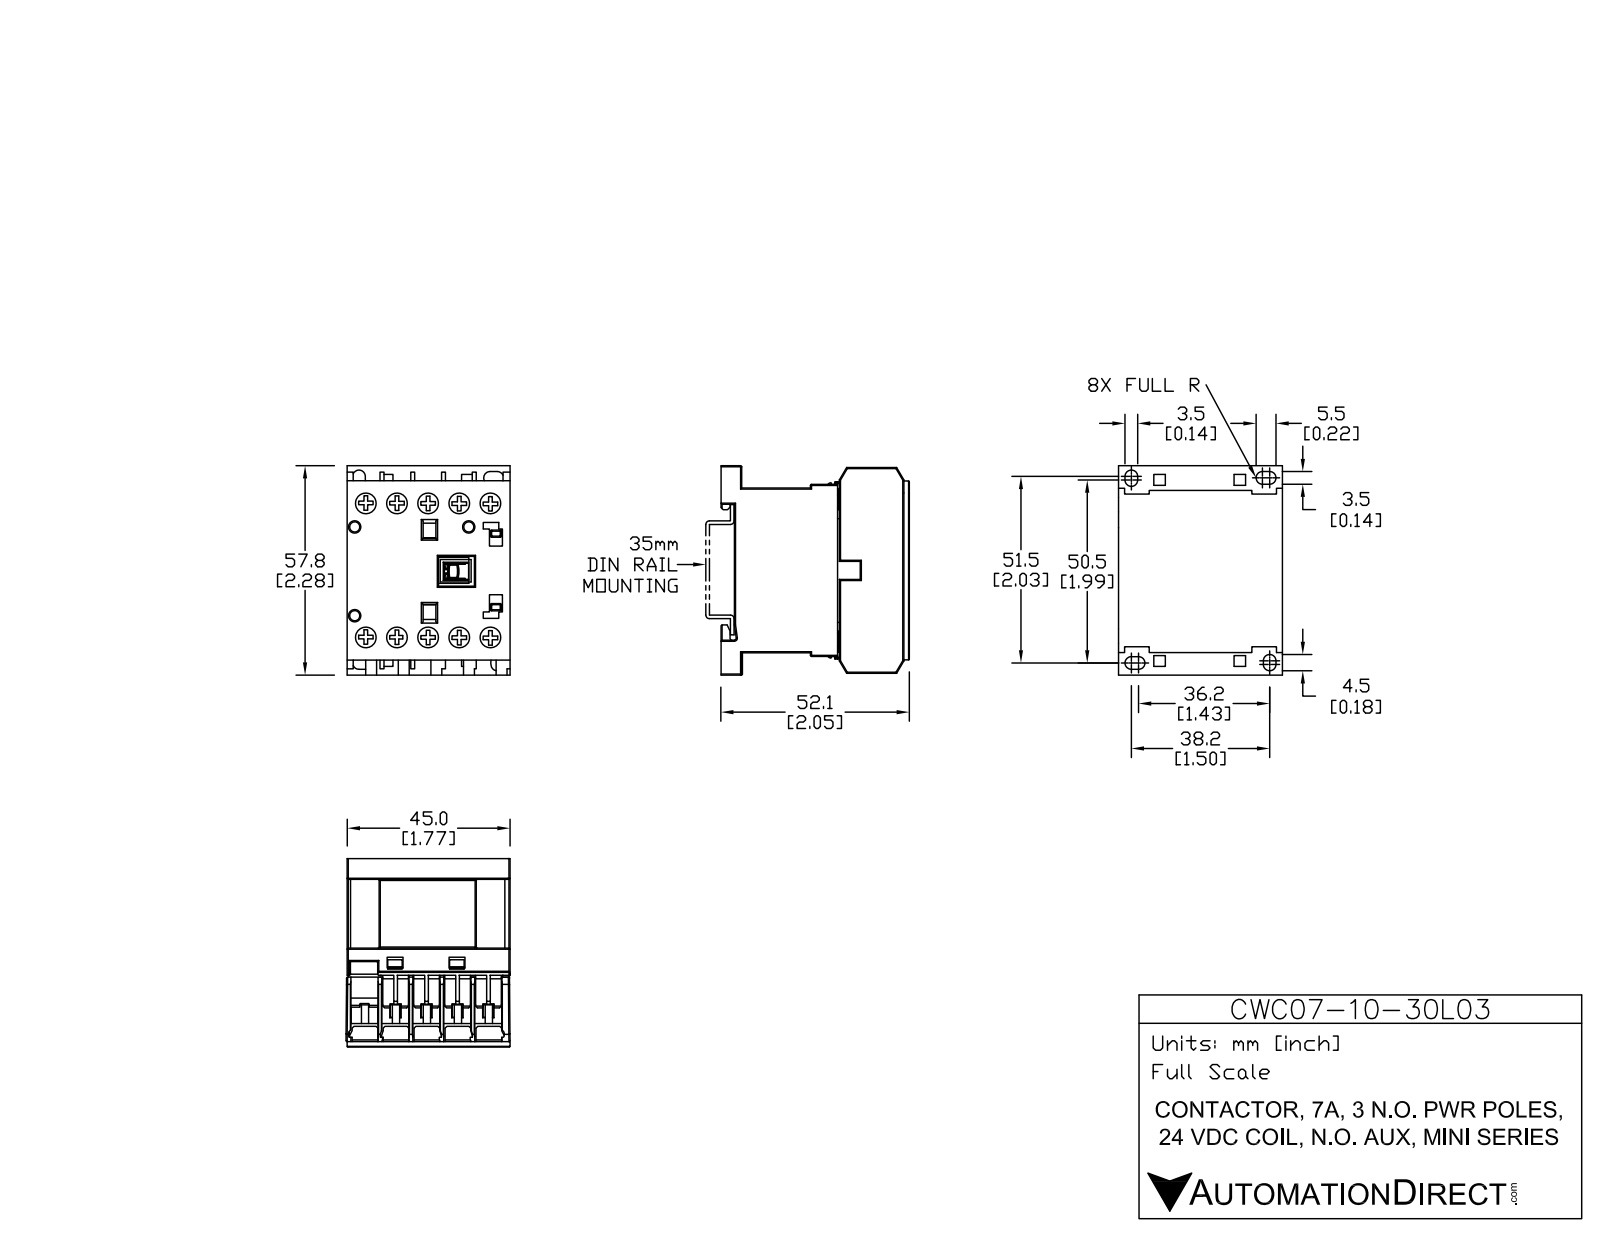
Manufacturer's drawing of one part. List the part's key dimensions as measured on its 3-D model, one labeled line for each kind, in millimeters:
Part name (STEP PRODUCT): CWC07-10-30L03
STEP written by: SolidWorks 2013 (AUTOMOTIVE_DESIGN)
Units: millimetres
Bodies: 15 solids, 535 faces (445 planar, 90 cylindrical, 0 other)
Overall size (bounding box): 58.04 × 52.12 × 45.75
Volume: 97 133 mm³ · Surface area: 30 437 mm²
Round holes (diameter × count): ⌀6.2 ×10, ⌀2.8 ×3
Round bosses / shafts (diameter × count): ⌀5.9 ×10
Partial cylindrical surfaces — rounded edges, fillets, slot ends (radius × count): R0.3 ×20, R1.72 ×6, R1.73 ×2, R0.32 ×1, R0.42 ×1, R0.55 ×1
Main face-to-face distances: 8.25, 45.5, 1.25, 16.5, 9.5, 5.5, 17.75, 5.13, 10.63, 7
Hole centre spacings: 8.55, 37.94, 17.1, 40.72, 36.96, 25.65, 44.99, 6.91
